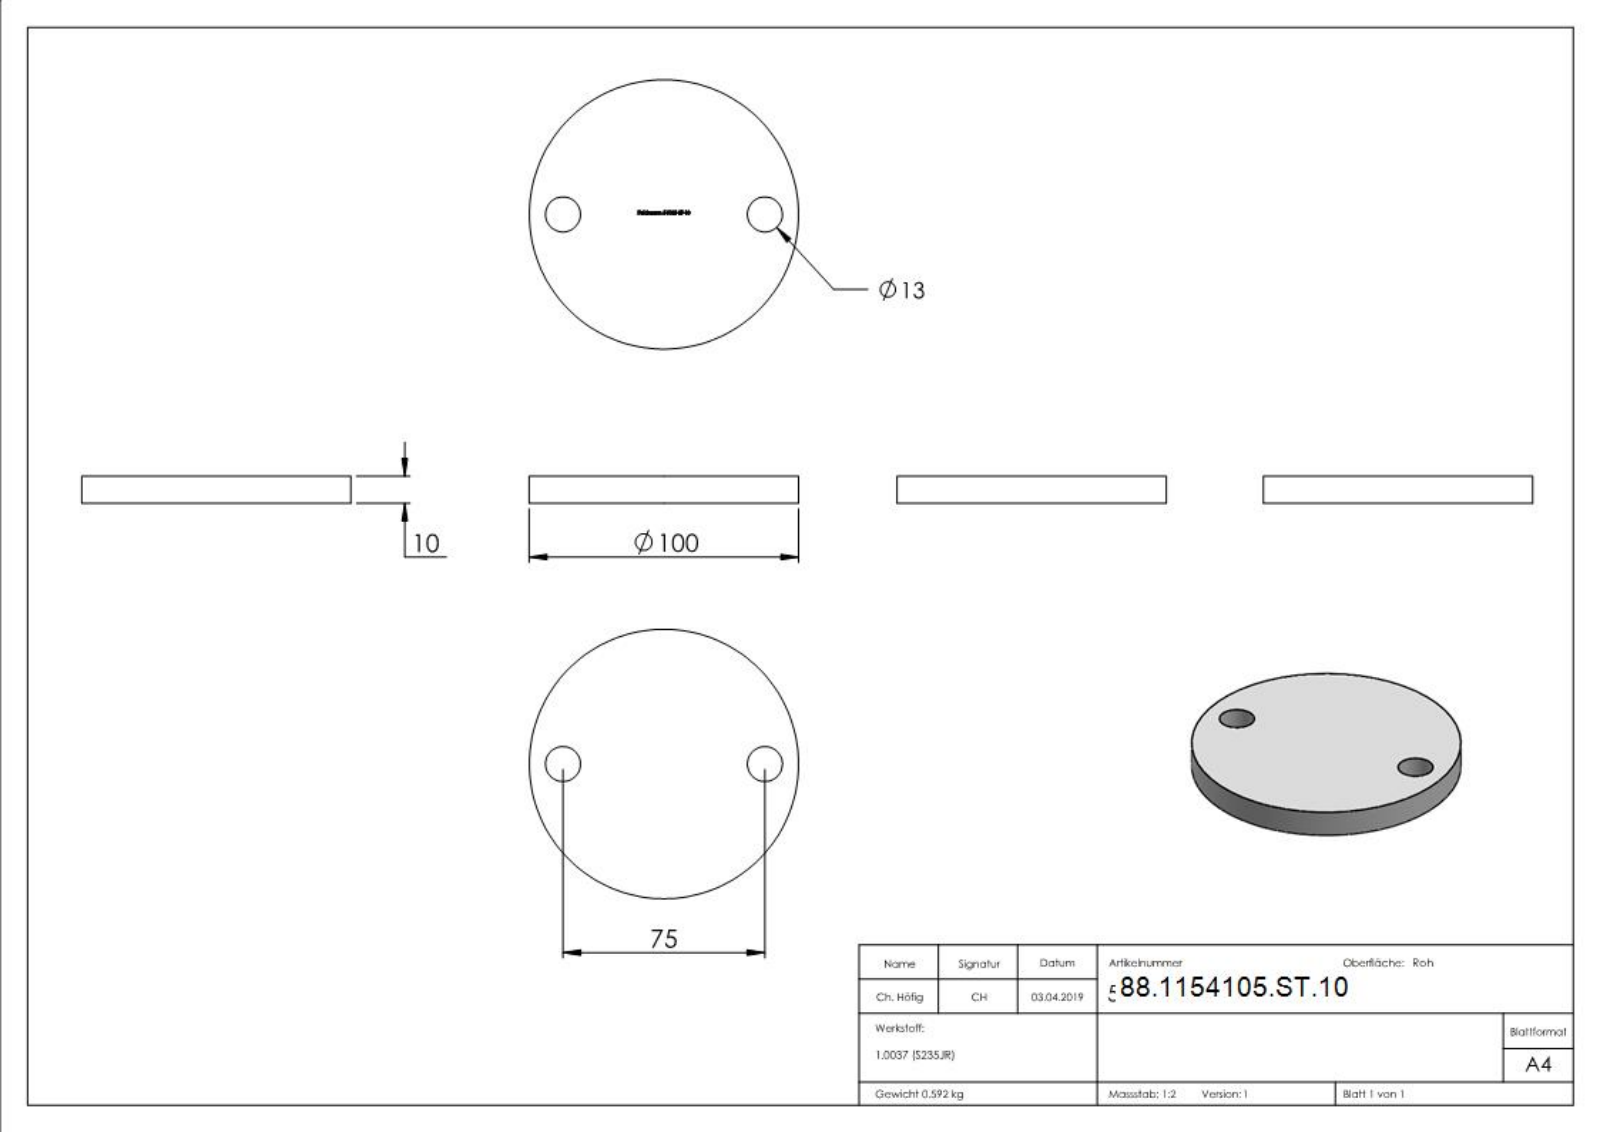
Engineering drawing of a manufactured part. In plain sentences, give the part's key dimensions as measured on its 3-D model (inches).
The part is named "54105-ST-10". Its 3-D file was written by "SolidWorks 2015 (CONFIG_CONTROL_DESIGN)". It is 1 solid with 239 faces: 136 planar, 6 cylindrical and 97 other. Overall it measures 3.937 by 3.937 by 0.394 inches. Its volume is 4.631 cubic inches and its surface area 29.67 square inches. Round holes: 2 of diameter 0.512. Round bosses or shafts: 1 of diameter 3.937. The main face-to-face distances are 0.394, 0.39, 0.383, 0.616, 0.233, 0.117, 0.08, 0.557, 0.174, 0.059. The hole center spacings are 2.953.
